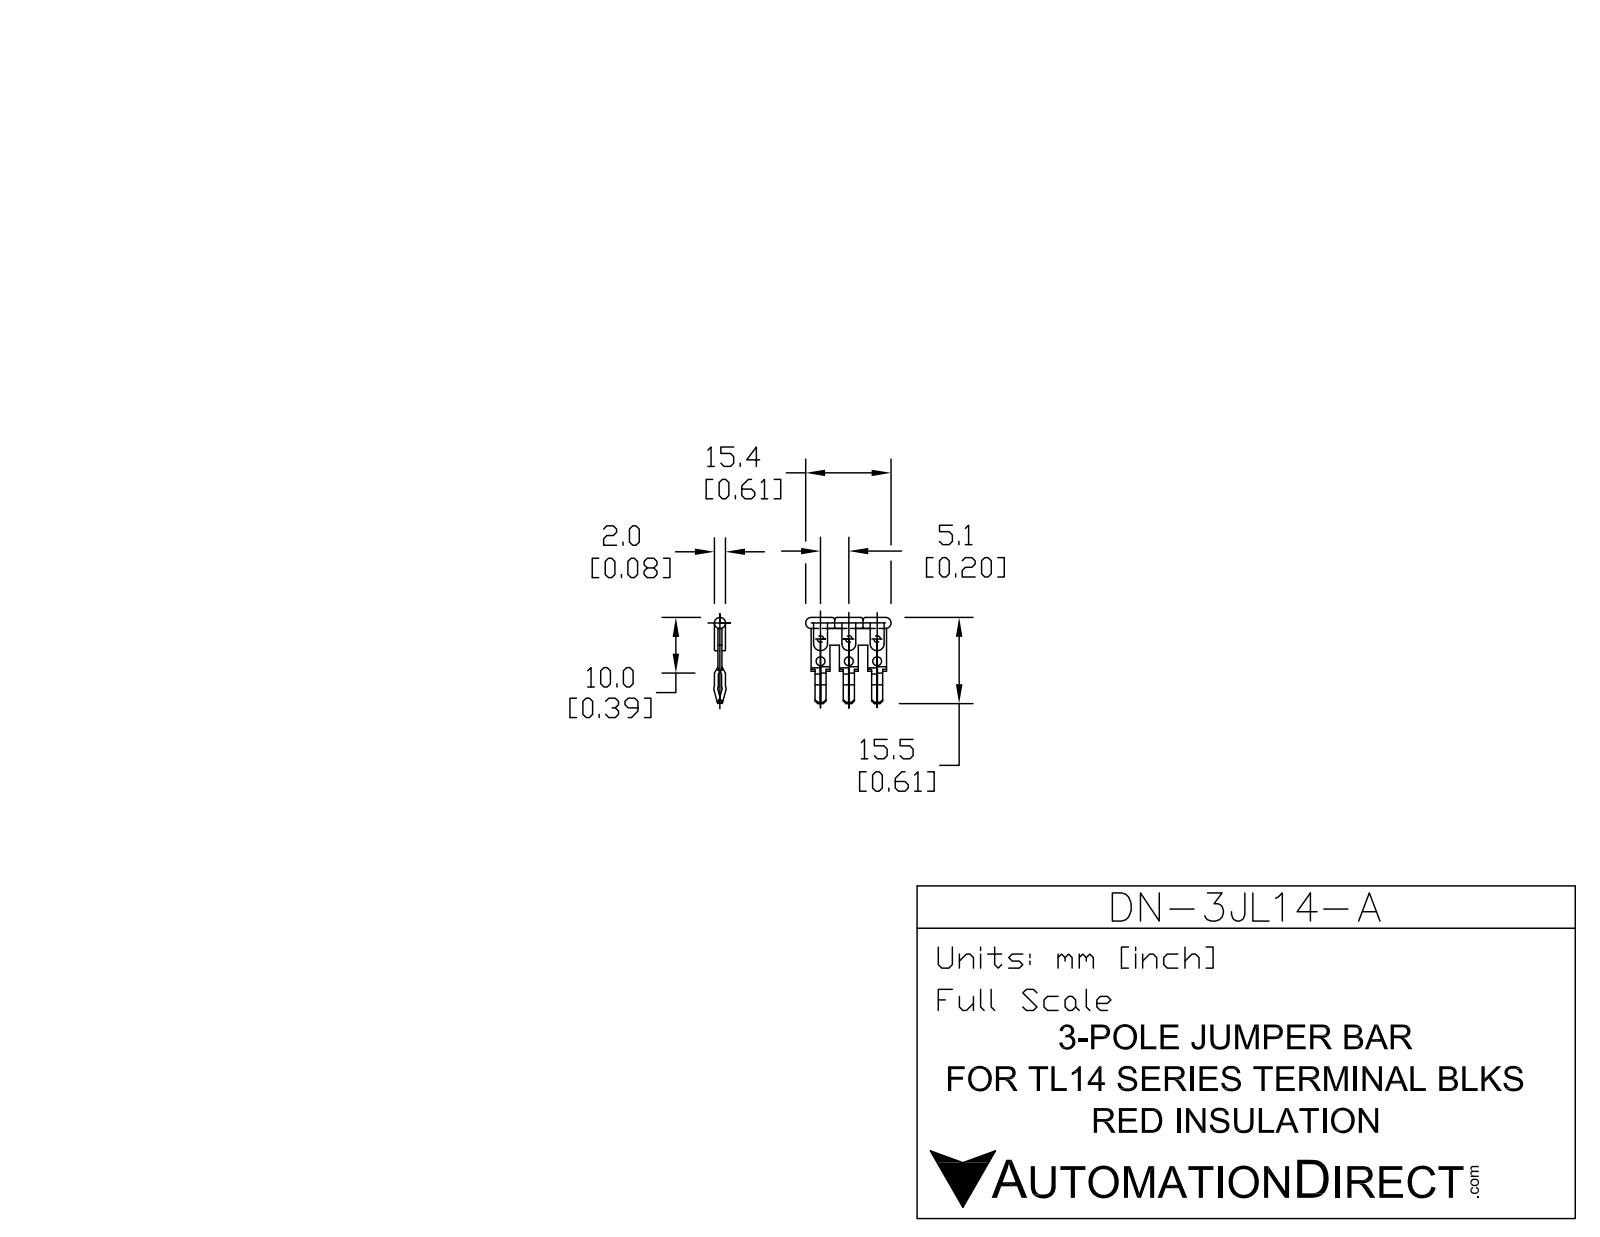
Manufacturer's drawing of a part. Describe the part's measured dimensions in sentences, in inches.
The part is named "43531_03_RDS_DN-3JL14-A". Its 3-D file was written by "SolidWorks 2013 (AUTOMOTIVE_DESIGN)". It is 2 solids with 217 faces: 113 planar, 80 cylindrical and 24 other. Overall it measures 0.61 by 0.598 by 0.082 inches. Its volume is 0.011 cubic inches and its surface area 0.853 square inches. Round holes: 3 of diameter 0.047, 3 of diameter 0.051. Round bosses or shafts: 1 of diameter 0.079. Partial cylindrical surfaces (rounded edges, fillets, slot ends): 12 of radius 0.01, 4 of radius 0.019, 4 of radius 0.028, 3 of radius 0.02, 3 of radius 0.049. The main face-to-face distances are 0.028, 0.026, 0.053, 0.201, 0.047, 0.079, 0.022, 0.402, 0.051, 0.089. The hole center spacings are 0.201, 0.255, 0.157, 0.402, 0.431.
